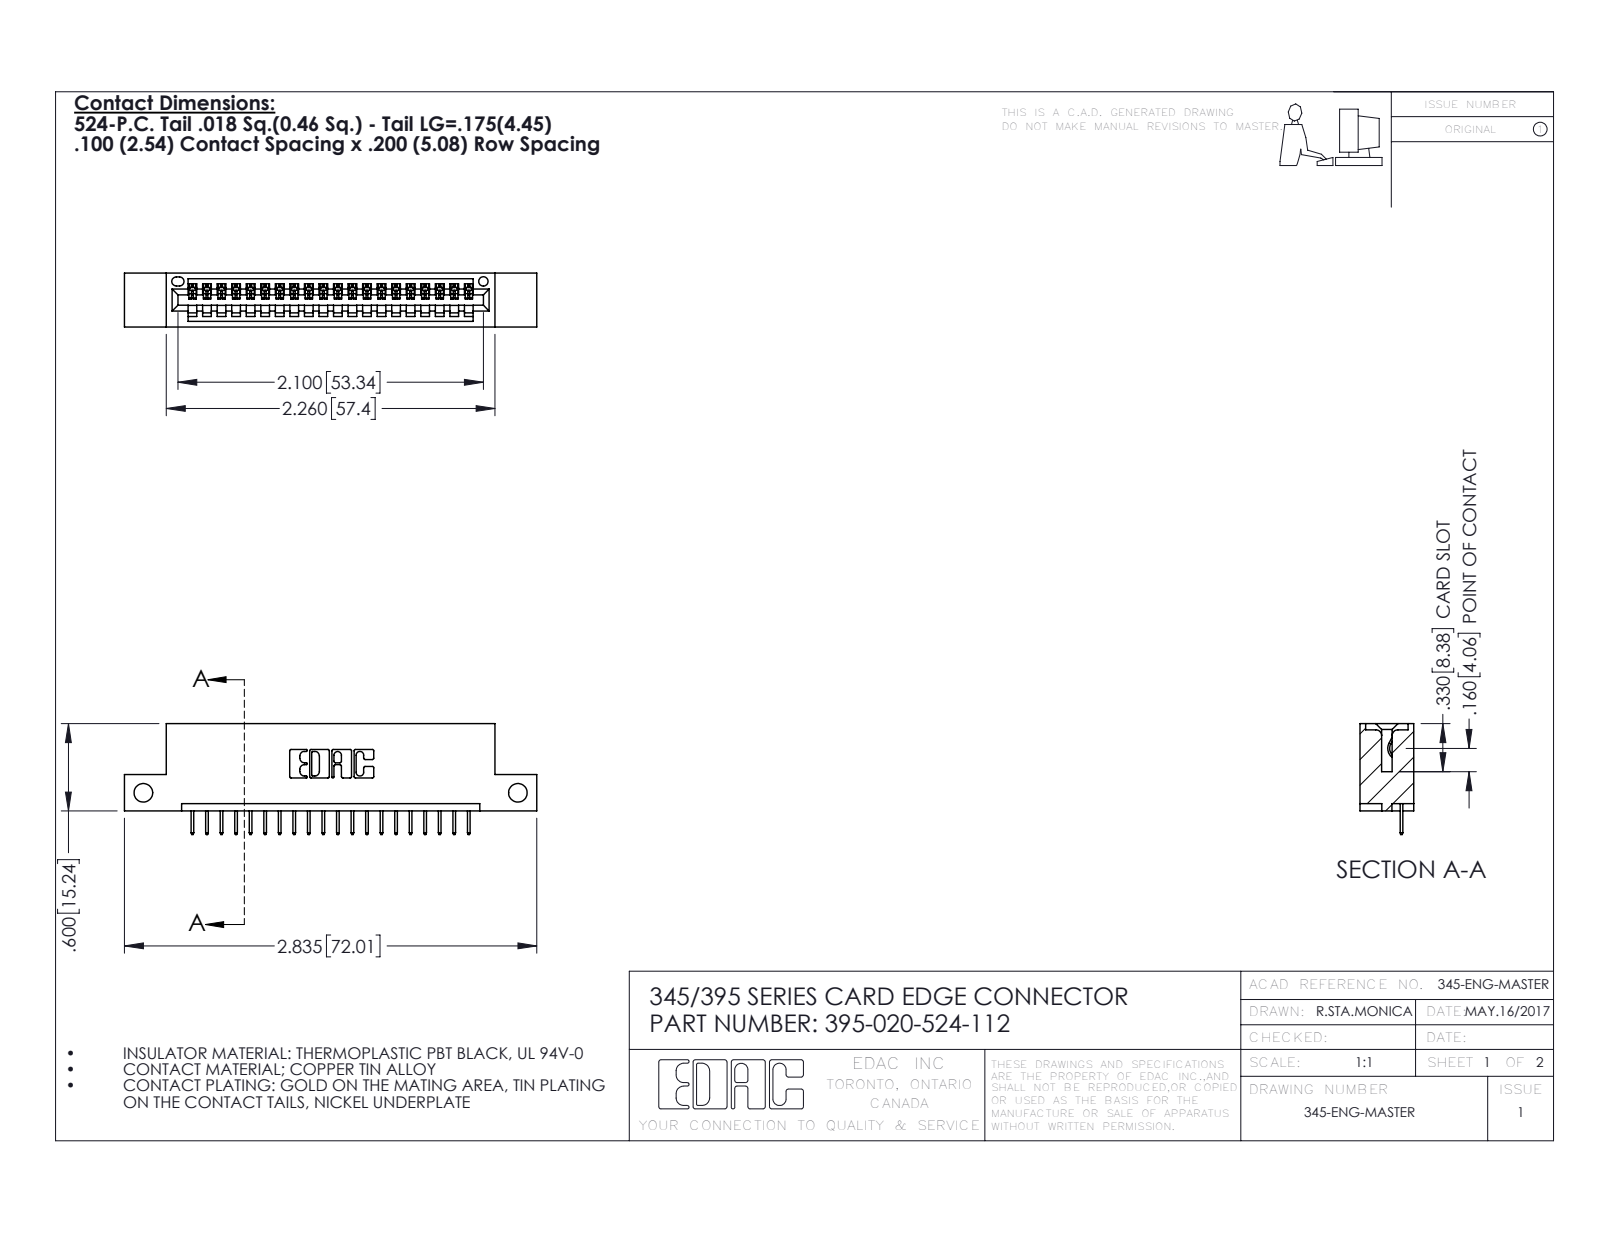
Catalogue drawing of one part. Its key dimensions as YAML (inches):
part_name: "395-020-524-112; 345-292-001_345-293-124; 345 Part_Flush Mounting Lugs - Side Mount"
step_written_by: "SolidWorks 2016 (CONFIG_CONTROL_DESIGN)"
units: inches
bodies: {solids: 21, faces: 1366, planar: 1000, cylindrical: 366, other: 0}
overall_size: [2.835, 0.762, 0.37]
volume: 0.396
surface_area: 12.3
round_holes:
  - {diameter: 0.128, count: 2}
  - {diameter: 0.064, count: 1}
partial_cylinders:
  - {radius: 0.006, count: 40}
  - {radius: 0.01, count: 22}
  - {radius: 0.007, count: 6}
  - {radius: 0.031, count: 6}
  - {radius: 0.026, count: 3}
  - {radius: 0.031, count: 2}
  - {radius: 0.04, count: 2}
  - {radius: 0.014, count: 1}
face_to_face_distances: [0.298, 0.072, 0.2, 0.37, 0.098, 0.272, 0.025, 0.225, 0.072, 0.149]
hole_center_spacings: [2.575]
